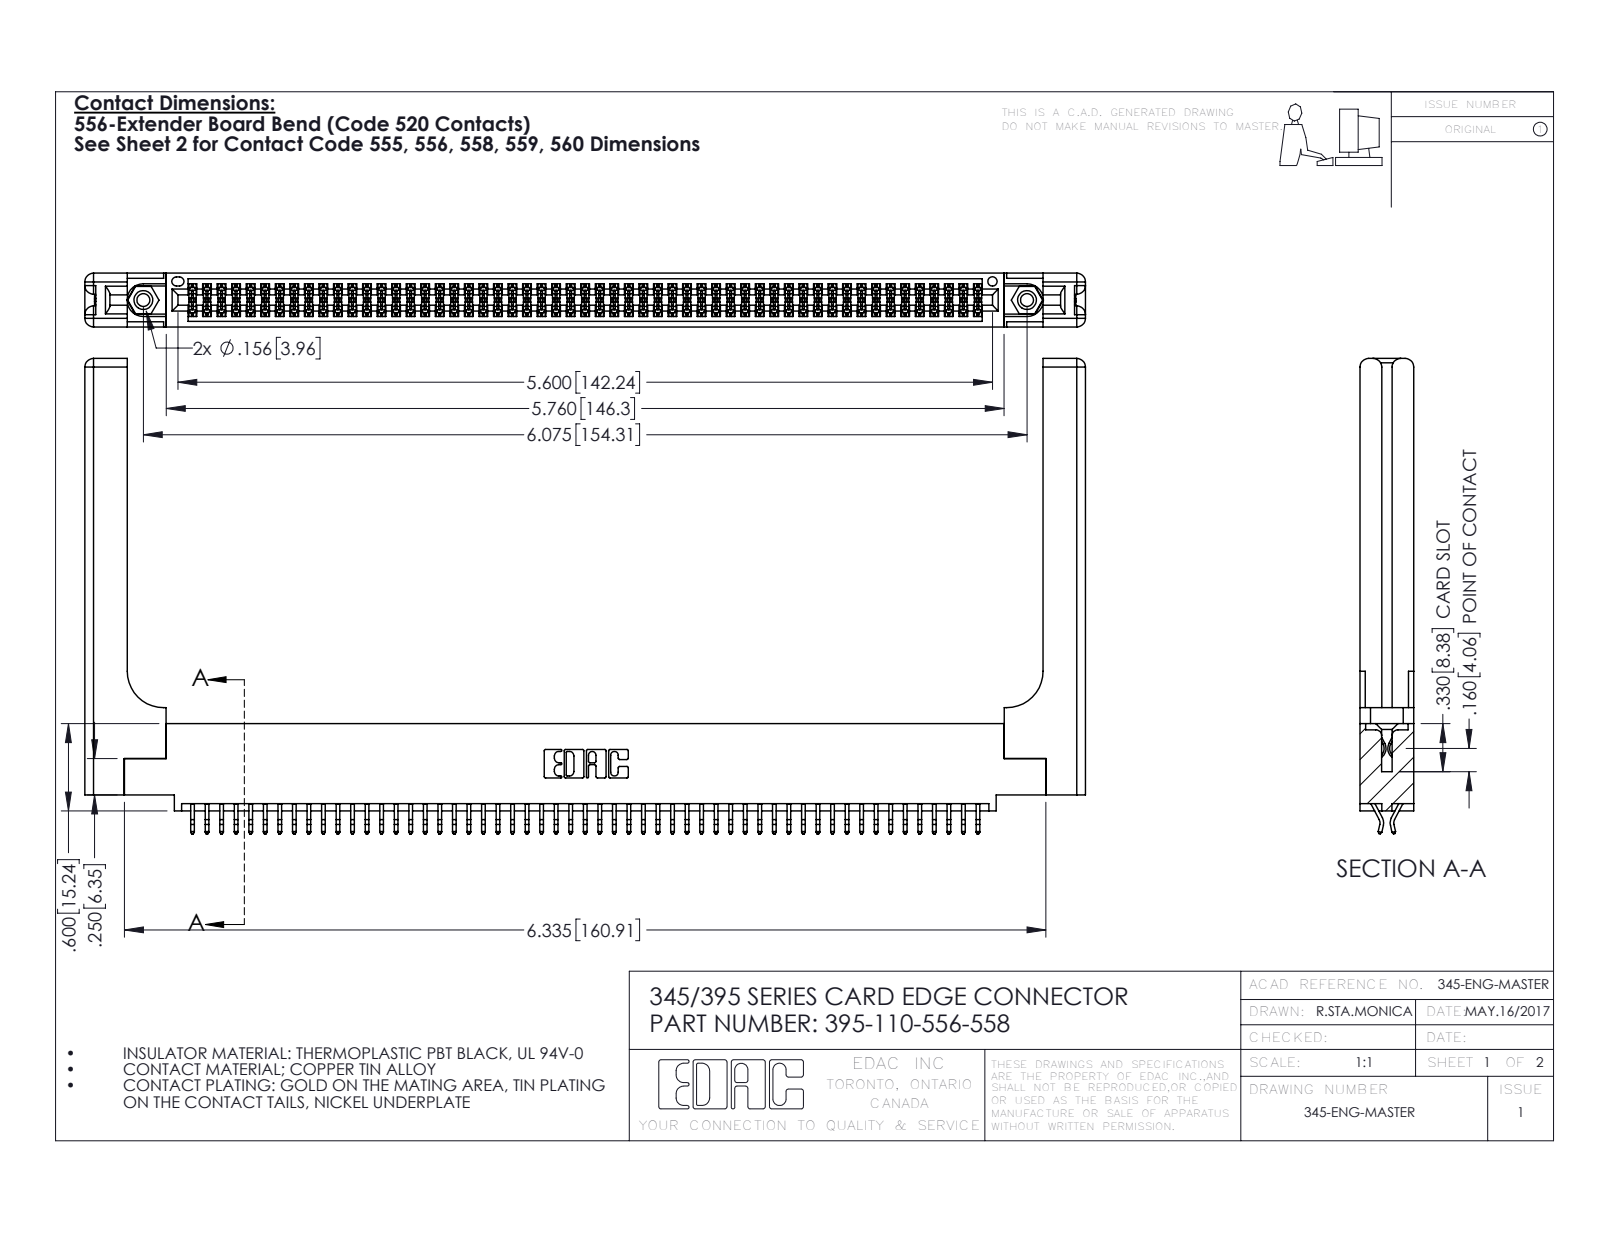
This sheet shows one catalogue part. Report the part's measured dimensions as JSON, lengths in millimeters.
{"part_name": "345 Part_0.110 Offset - 0.156 Dia-TH; 395-110-556-558; 345-250-001_345-250-001-102; 345-220-058_345-220-058 (+1 more)", "step_written_by": "SolidWorks 2016 (CONFIG_CONTROL_DESIGN)", "units": "millimeters", "bodies": {"solids": 115, "faces": 6546, "planar": 4302, "cylindrical": 2184, "other": 60}, "overall_size": [174.7, 83, 9.4], "volume_mm3": 25500, "surface_area_mm2": 30460, "round_holes": [[2.3, 2], [3.2, 2], [4, 2], [1.6, 1]], "round_bosses_or_shafts": [[3.9, 2]], "partial_cylinders_radius": [[0.2, 165], [0.3, 22], [1.5, 16], [0.2, 6], [0.8, 6], [0.7, 3], [0.3, 2], [0.4, 2]], "face_to_face_distances": [1.8, 7.6, 9.4, 0.6, 2.5, 6.9, 5.1, 5.7, 3.8, 3.8], "hole_center_spacings": [6.9, 148.3, 154.3]}
